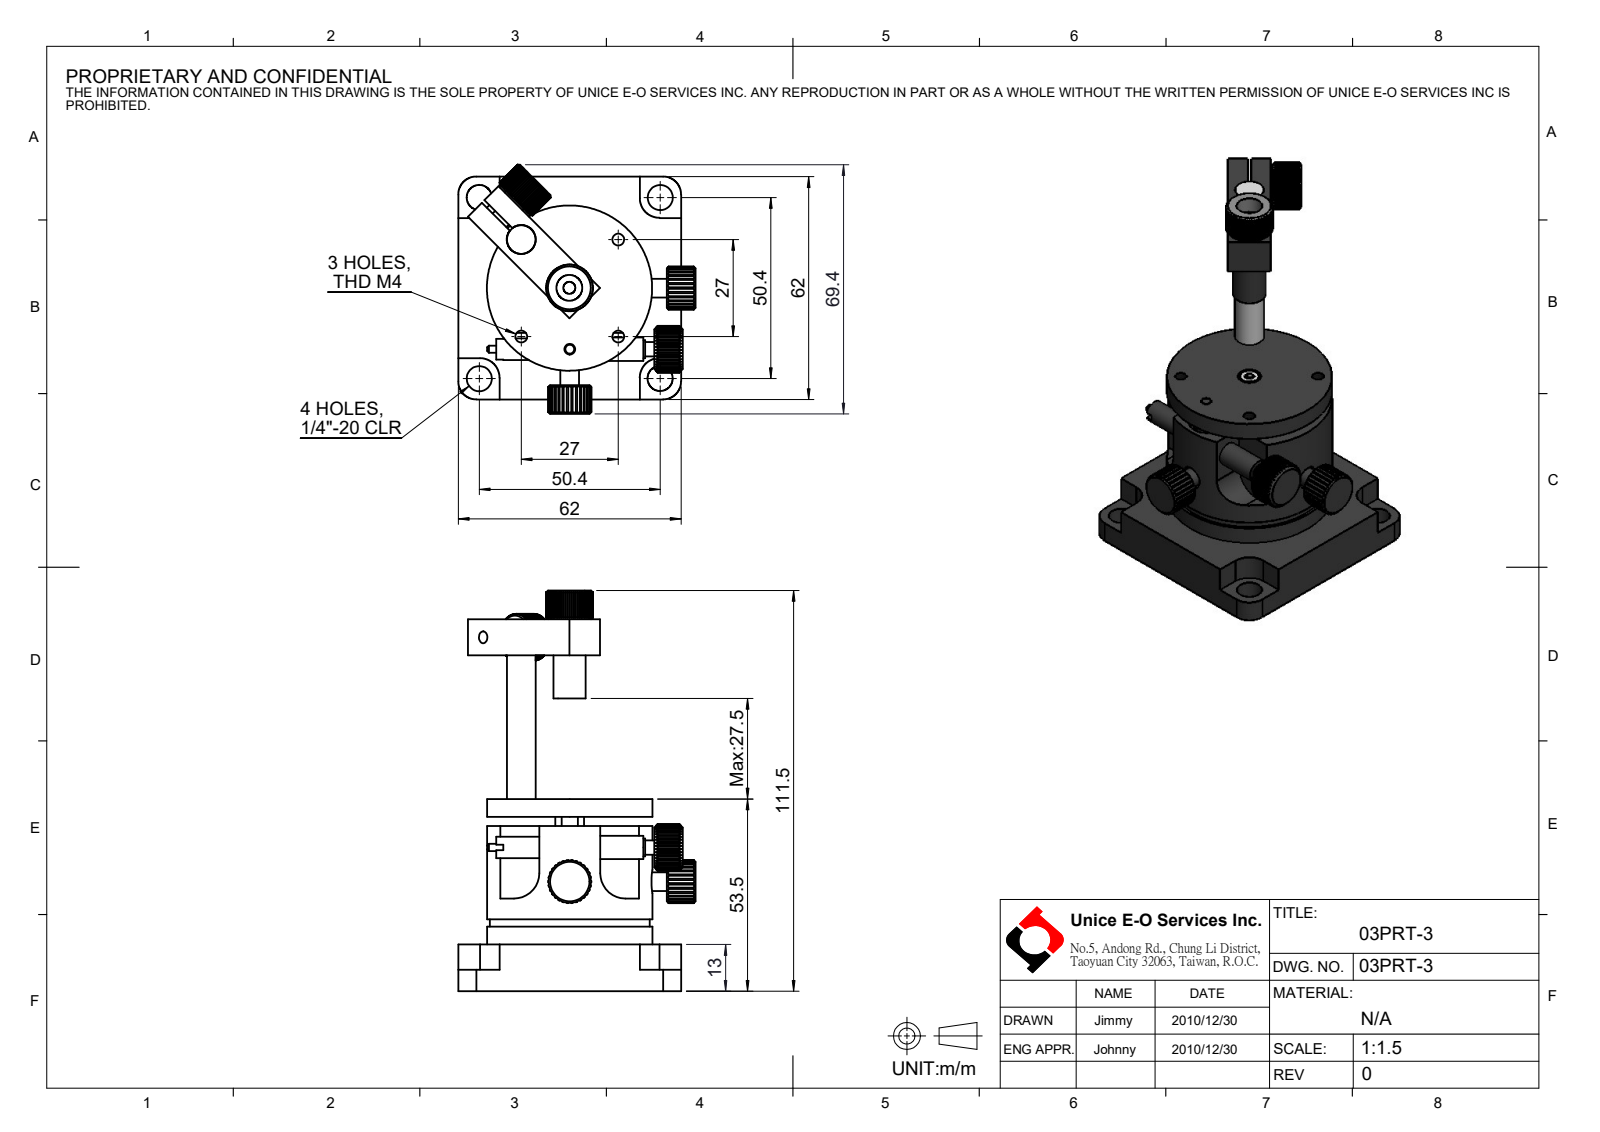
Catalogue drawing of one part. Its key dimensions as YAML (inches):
part_name: "03PRT-3"
step_written_by: "SolidWorks 2016 (CONFIG_CONTROL_DESIGN)"
units: inches
bodies: {solids: 0, faces: 1174, planar: 213, cylindrical: 909, other: 52}
overall_size: [4.39, 2.731, 2.598]
round_holes:
  - {diameter: 0.13, count: 7}
  - {diameter: 0.256, count: 4}
  - {diameter: 0.276, count: 4}
  - {diameter: 0.315, count: 4}
  - {diameter: 0.283, count: 3}
  - {diameter: 0.083, count: 1}
  - {diameter: 0.374, count: 1}
round_bosses_or_shafts:
  - {diameter: 0.276, count: 2}
  - {diameter: 0.236, count: 2}
  - {diameter: 0.205, count: 2}
  - {diameter: 0.079, count: 2}
  - {diameter: 1.811, count: 1}
  - {diameter: 1.752, count: 1}
  - {diameter: 0.354, count: 1}
  - {diameter: 0.315, count: 1}
partial_cylinders:
  - {radius: 0.004, count: 177}
  - {radius: 0.03, count: 60}
  - {radius: 0.197, count: 4}
  - {radius: 0.217, count: 4}
  - {radius: 0.256, count: 4}
  - {radius: 0.236, count: 2}
  - {radius: 0.276, count: 2}
  - {radius: 0.098, count: 1}
face_to_face_distances: [0.512, 1.398, 0.197, 2.106, 1.909, 1.594, 1.299, 0.472, 0.295, 2.441]
hole_center_spacings: [1.566, 0.696, 1.024, 1.403, 1.592, 0.752, 0.707, 0.866]
